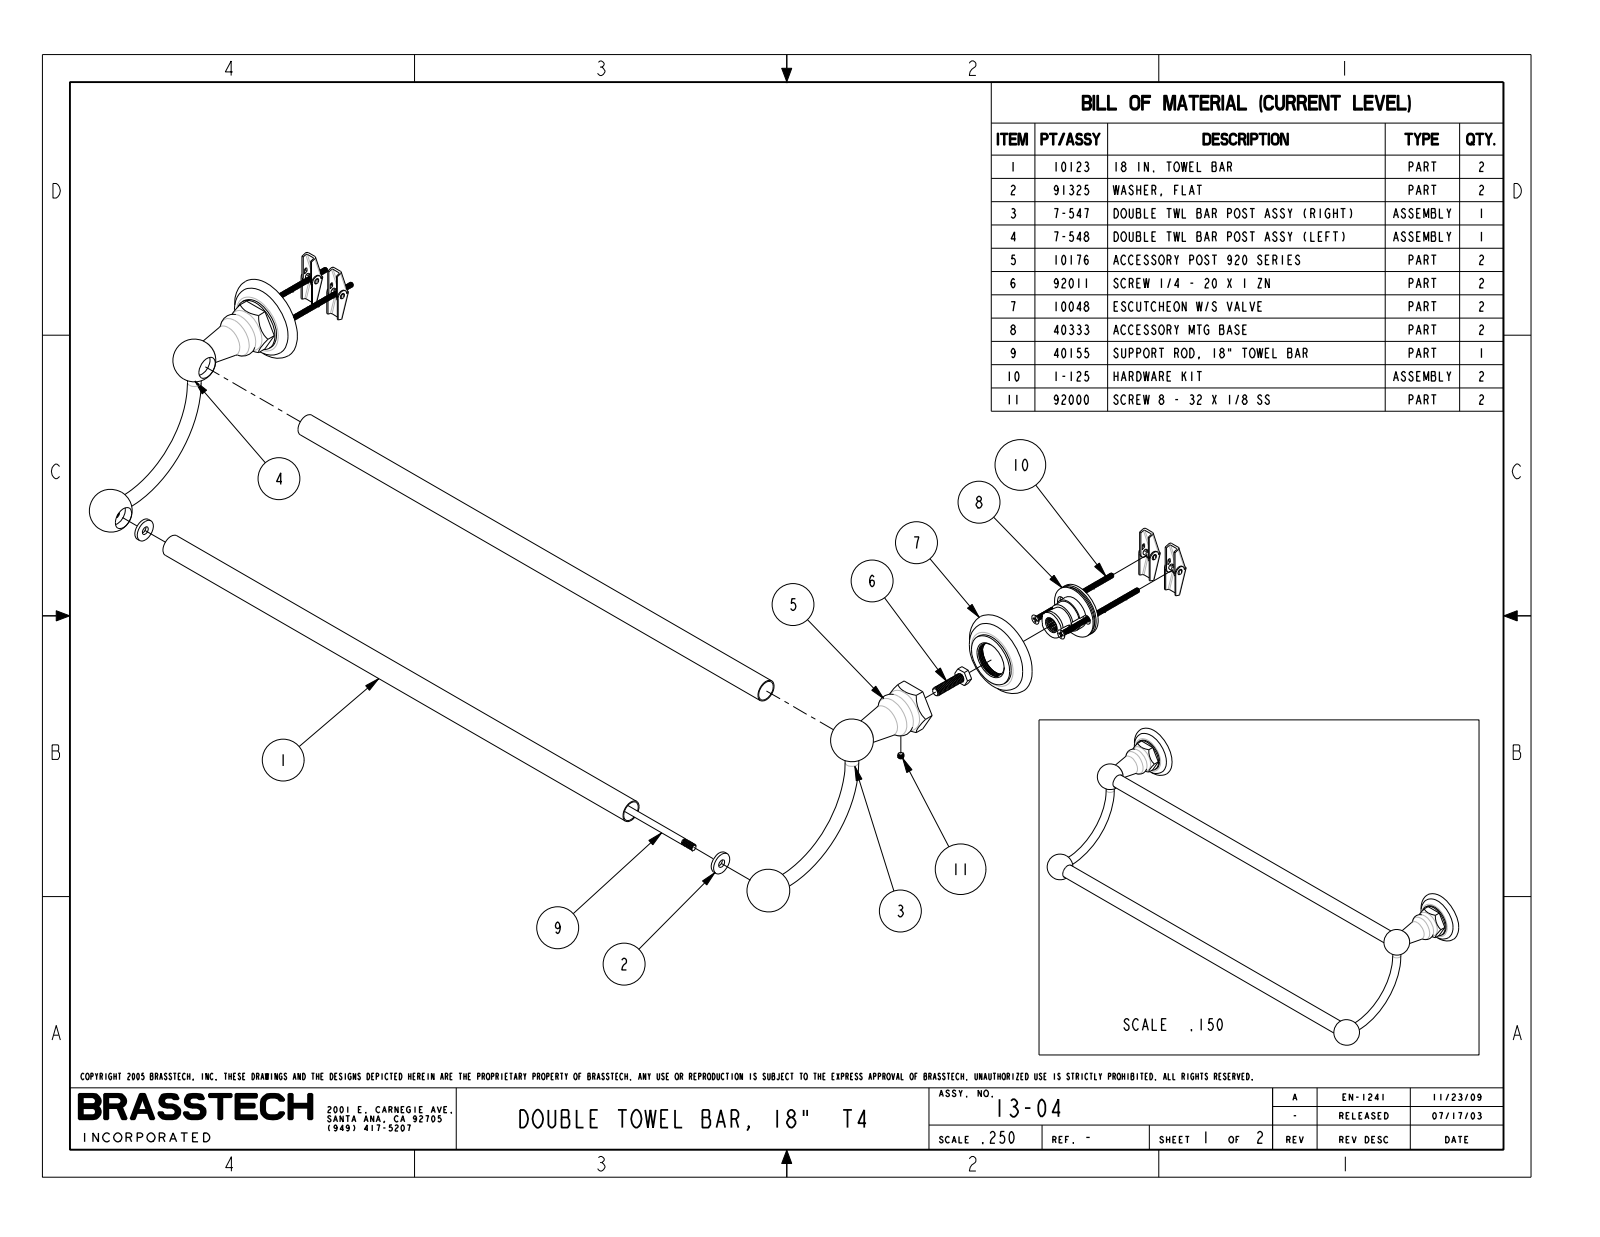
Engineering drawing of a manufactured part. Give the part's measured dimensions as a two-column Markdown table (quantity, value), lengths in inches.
| quantity | value |
| --- | --- |
| part name | 13-04_SW0001 |
| STEP written by | PRO/ENGINEER BY PARAMETRIC TECHNOLOGY CORPORATION, 2009300 (CONFIG_CONTROL_DESIGN) |
| units | inches |
| bodies | 0 solids, 110 faces (20 planar, 32 cylindrical, 58 other) |
| overall size | 20.936 × 6.667 × 5.201 |
| round holes (diameter × count) | 0.13 × 2, 0.635 × 2 |
| round bosses / shafts (diameter × count) | 1.482 × 2, 0.625 × 2, 0.375 × 2 |
| main face-to-face distances | 0.375, 0.437, 0.062, 1.25, 16.087, 14.837, 17.337, 0.1, 1.15 |
| hole center spacings | 4.728, 18.576 |
